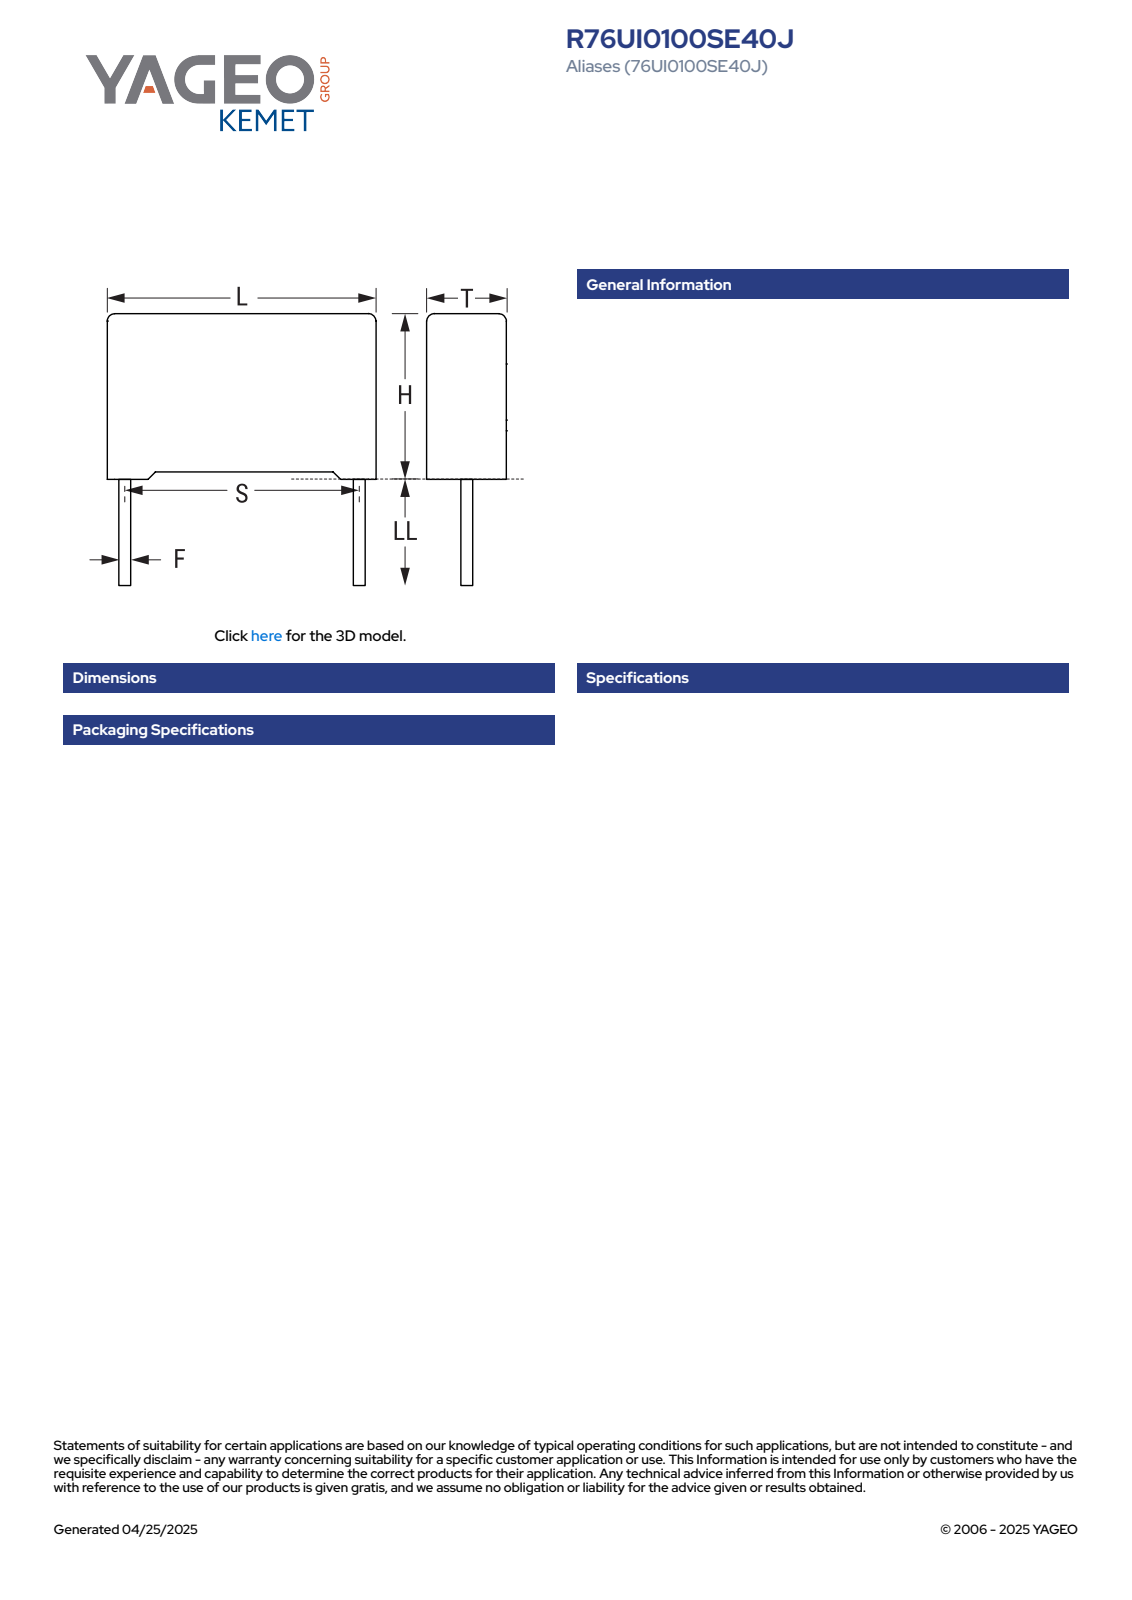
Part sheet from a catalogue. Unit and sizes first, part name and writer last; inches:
Units: inches
Overall size (bounding box): 0.72 × 0.634 × 0.166
Round bosses / shafts (diameter × count): ⌀0.033 ×2
Partial cylindrical surfaces — rounded edges, fillets, slot ends (radius × count): R0.02 ×4
Main face-to-face distances: 0.165, 0.368, 0.72, 0.024, 0.141, 0.016, 0.384, 0.03, 0.014, 0.398
Volume: 0.045 in³ · Surface area: 1.04 in²
Bodies: 4 solids, 85 faces (77 planar, 8 cylindrical, 0 other)
Part name (STEP PRODUCT): CFR_RB2_18X10X4_L18.3H10.1T4.2S15LL6F0.85
STEP written by: SolidWorks 2021 (AUTOMOTIVE_DESIGN)
